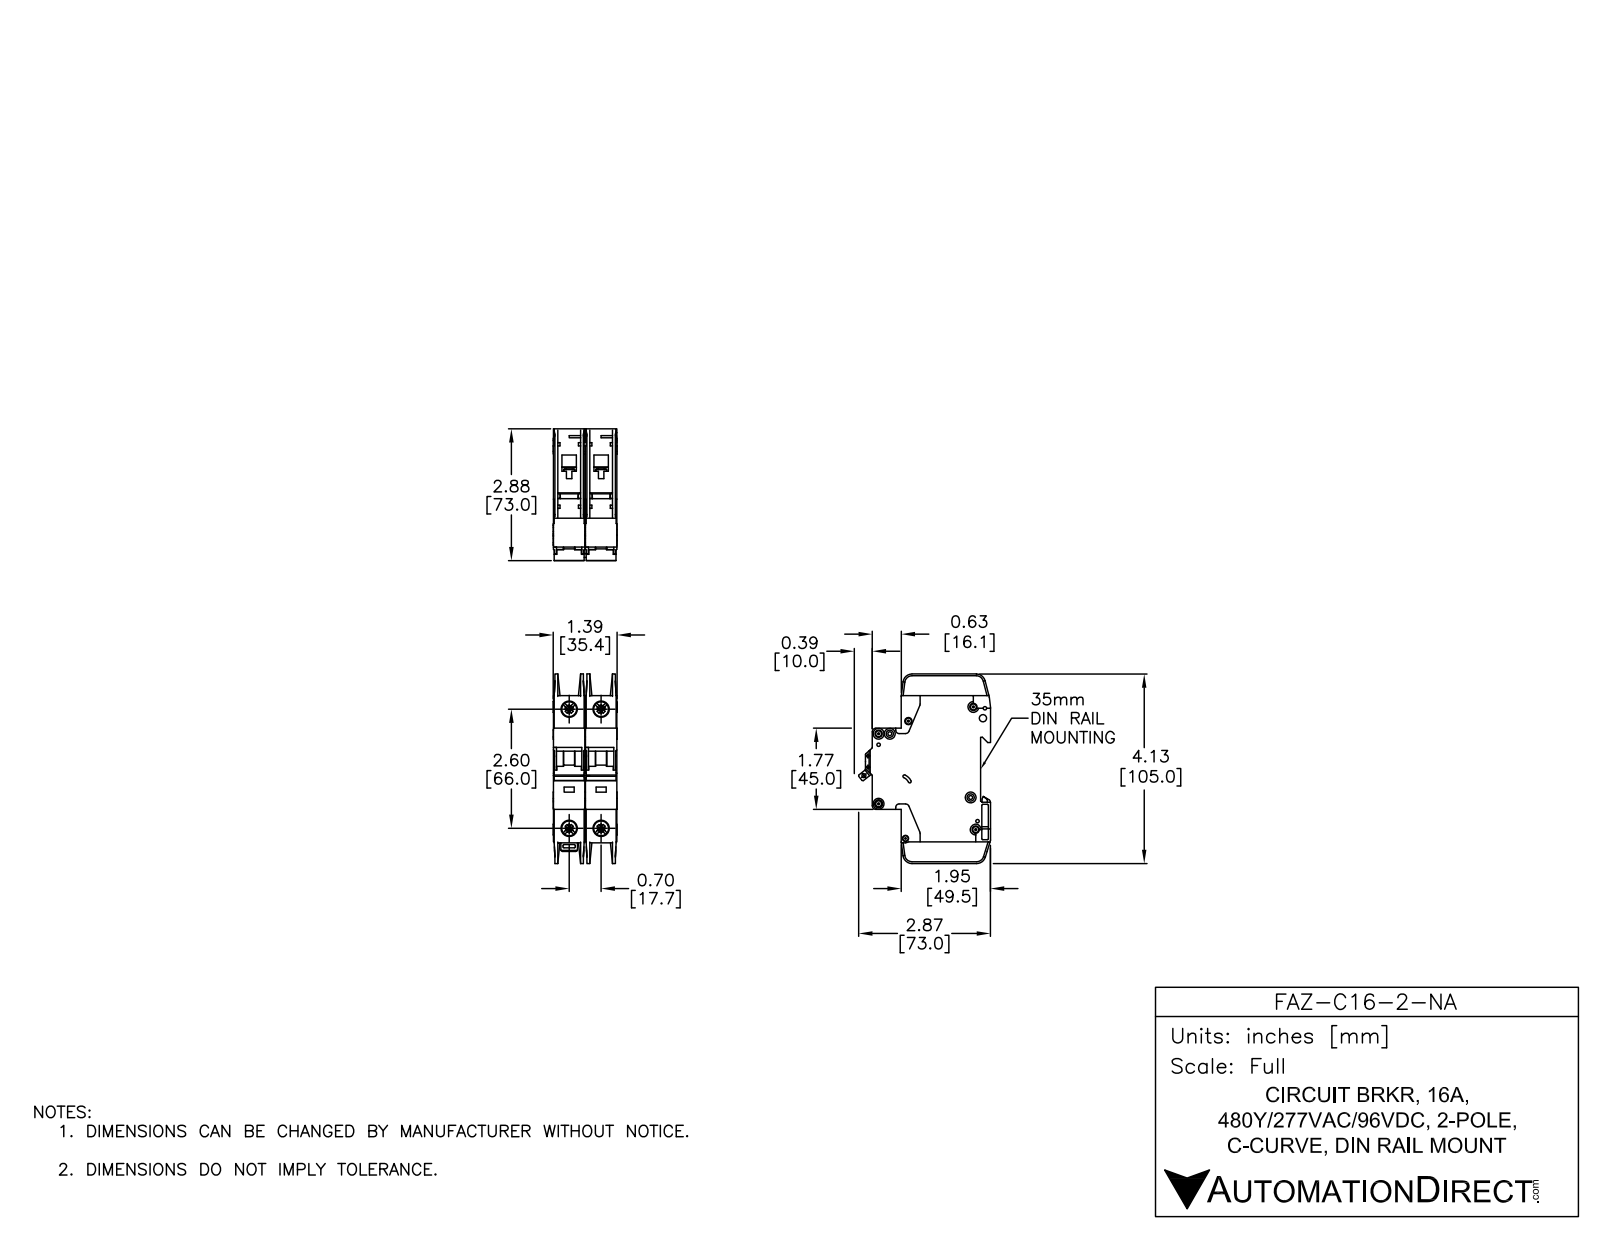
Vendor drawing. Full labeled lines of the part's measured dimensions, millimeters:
Part name (STEP PRODUCT): FAZ-C16-2-NA
STEP written by: SolidWorks 2014 (AUTOMOTIVE_DESIGN)
Units: millimetres
Bodies: 6 solids, 1568 faces (818 planar, 526 cylindrical, 224 other)
Overall size (bounding box): 105 × 73.04 × 35.4
Volume: 155 390 mm³ · Surface area: 49 479 mm²
Round holes (diameter × count): ⌀3.6 ×7, ⌀7.15 ×4, ⌀8.2 ×4, ⌀1.09 ×2, ⌀1.5 ×2, ⌀4 ×2, ⌀1.9 ×1, ⌀2.15 ×1, ⌀2.2 ×1, ⌀2.55 ×1, ⌀3.3 ×1, ⌀3.4 ×1
Round bosses / shafts (diameter × count): ⌀6 ×7, ⌀2.5 ×2
Partial cylindrical surfaces — rounded edges, fillets, slot ends (radius × count): R0.25 ×47, R0.5 ×24, R1 ×18, R2 ×12, R5 ×5, R1.8 ×4, R4 ×4, R0.2 ×2
Main face-to-face distances: 17.7, 17.5, 0.7, 15.05, 2.45, 1.75, 15.75, 13.3, 35.2, 17
Hole centre spacings: 6.2, 17.7, 66, 68.33, 5.19, 6.1, 8.19, 8.56
